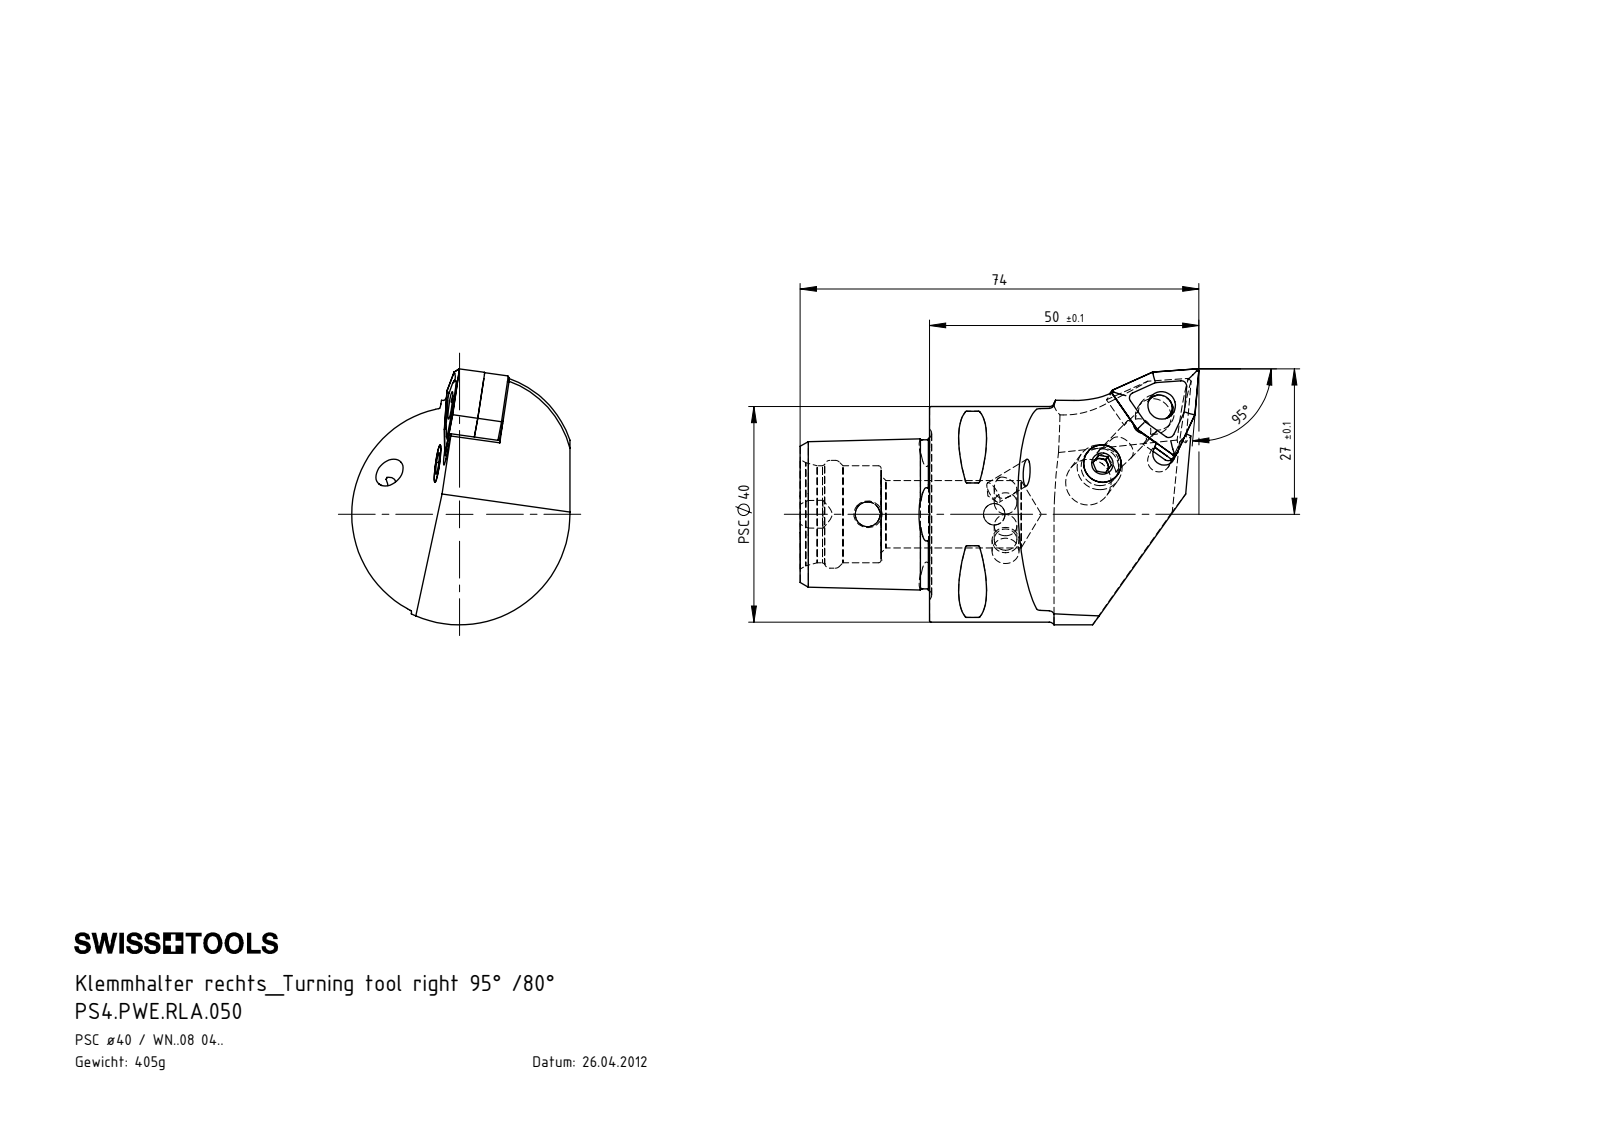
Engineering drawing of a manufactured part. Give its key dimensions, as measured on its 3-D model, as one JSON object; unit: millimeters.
{"part_name": "WCD-ER1.101.000; WCD-ER4.101.017_A; WNMG080404; WDF-ER3.101.000_A (+4 more)", "step_written_by": "SolidWorks 2017 (AUTOMOTIVE_DESIGN)", "units": "millimeters", "bodies": {"solids": 8, "faces": 372, "planar": 102, "cylindrical": 87, "other": 183}, "overall_size": [74, 47.5, 40.5], "volume_mm3": 50932, "surface_area_mm2": 15763, "round_holes": [[4, 2], [4.2, 2], [4.6, 1], [5, 1], [5.16, 1], [6.7, 1], [7, 1], [7.8, 1], [8.4, 1], [12.5, 1], [18, 1], [20, 1]], "round_bosses_or_shafts": [[40, 1], [8, 1], [7.9, 1], [6.4, 1], [5, 1], [4.7, 1], [3.55, 1]], "partial_cylinders_radius": [[0.3, 8], [0.4, 3], [1, 3], [2.5, 3], [0.8, 1], [2.1, 1], [2.3, 1], [2.35, 1]], "face_to_face_distances": [9.25, 4.77, 4.76, 24, 4.48, 15.52, 4.49, 0.4, 5, 6.3], "hole_center_spacings": [15.6, 15.61, 23.5]}
